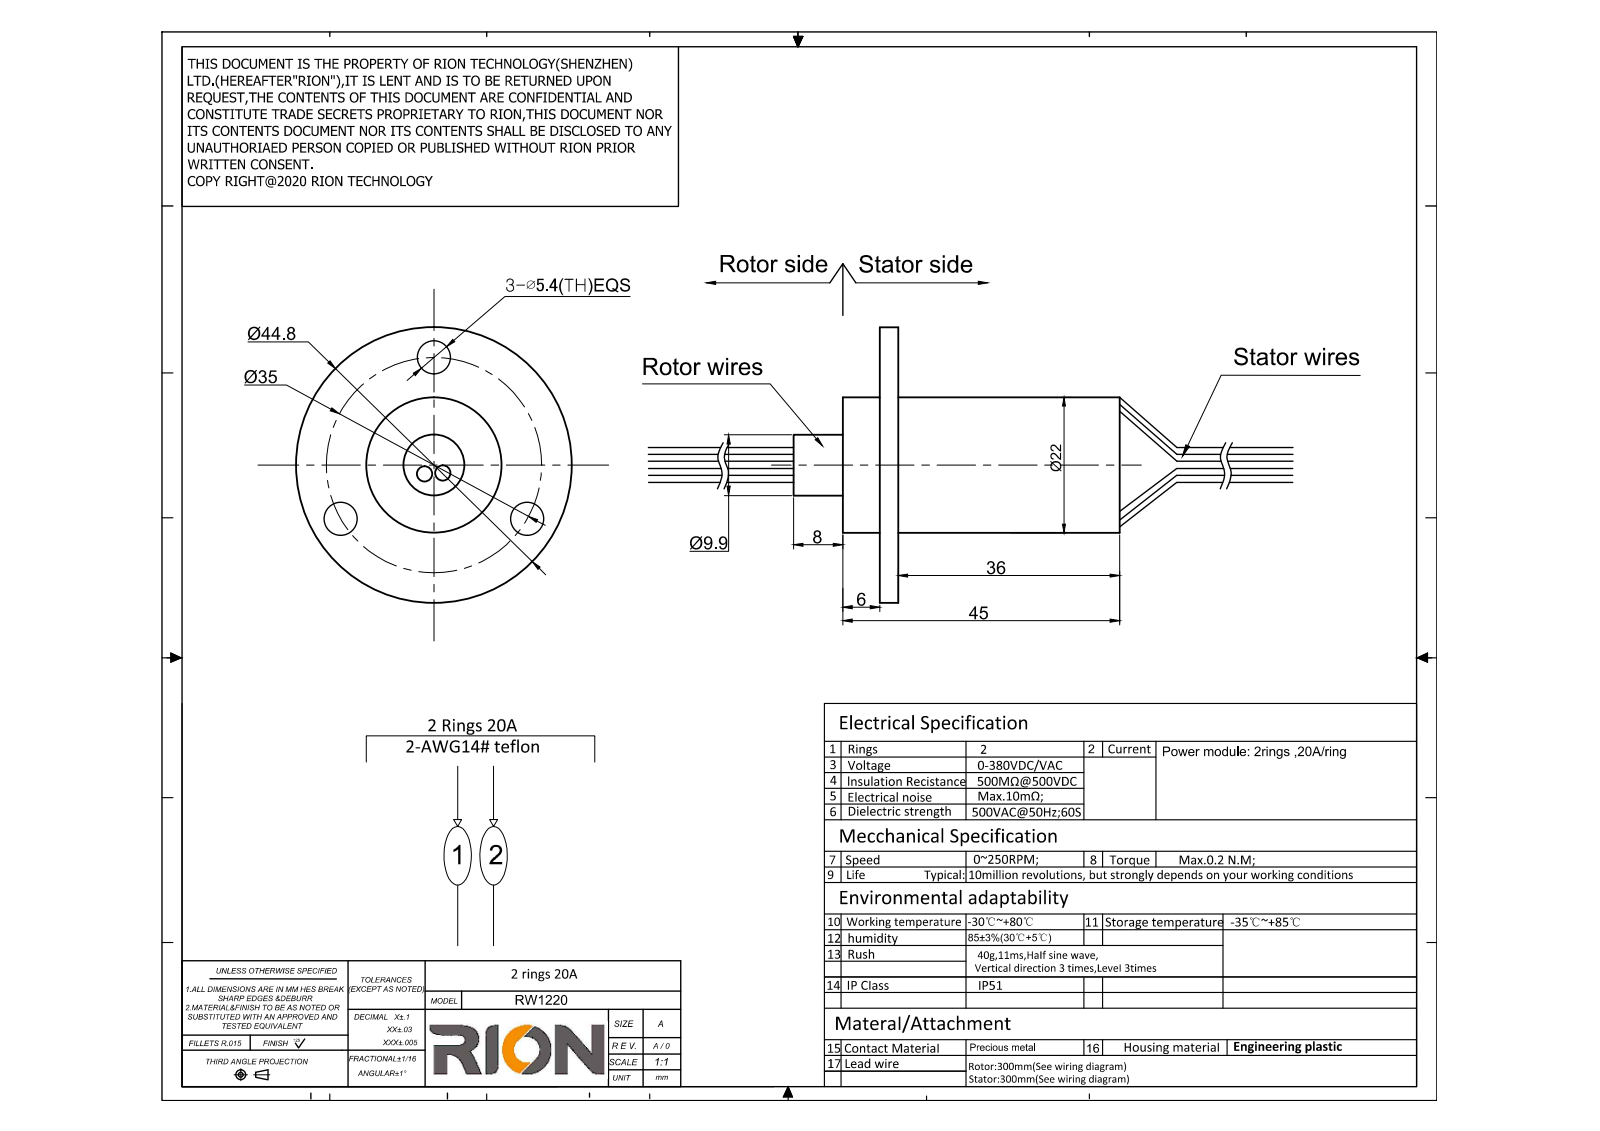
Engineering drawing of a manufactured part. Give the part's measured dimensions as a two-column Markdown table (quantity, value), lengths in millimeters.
| quantity | value |
| --- | --- |
| part name | Admi41D825DBra7z |
| STEP written by | SIEMENS PLM Software NX 8.5 (AUTOMOTIVE_DESIGN) |
| units | millimeters |
| bodies | 1 solid, 51 faces (21 planar, 30 cylindrical, 0 other) |
| overall size | 92.7 × 44.8 × 44.8 |
| volume | 21 479 mm³ |
| surface area | 7 625 mm² |
| round holes (diameter × count) | 5.4 × 3, 6.62 × 1, 10.1 × 1, 20 × 1 |
| round bosses / shafts (diameter × count) | 2.5 × 4, 44.8 × 1, 22 × 1, 19.9 × 1, 9.9 × 1 |
| main face-to-face distances | 3, 39, 36, 6, 9, 45, 8, 14, 17, 53 |
| hole center spacings | 17.5, 30.31, 30.32 |
